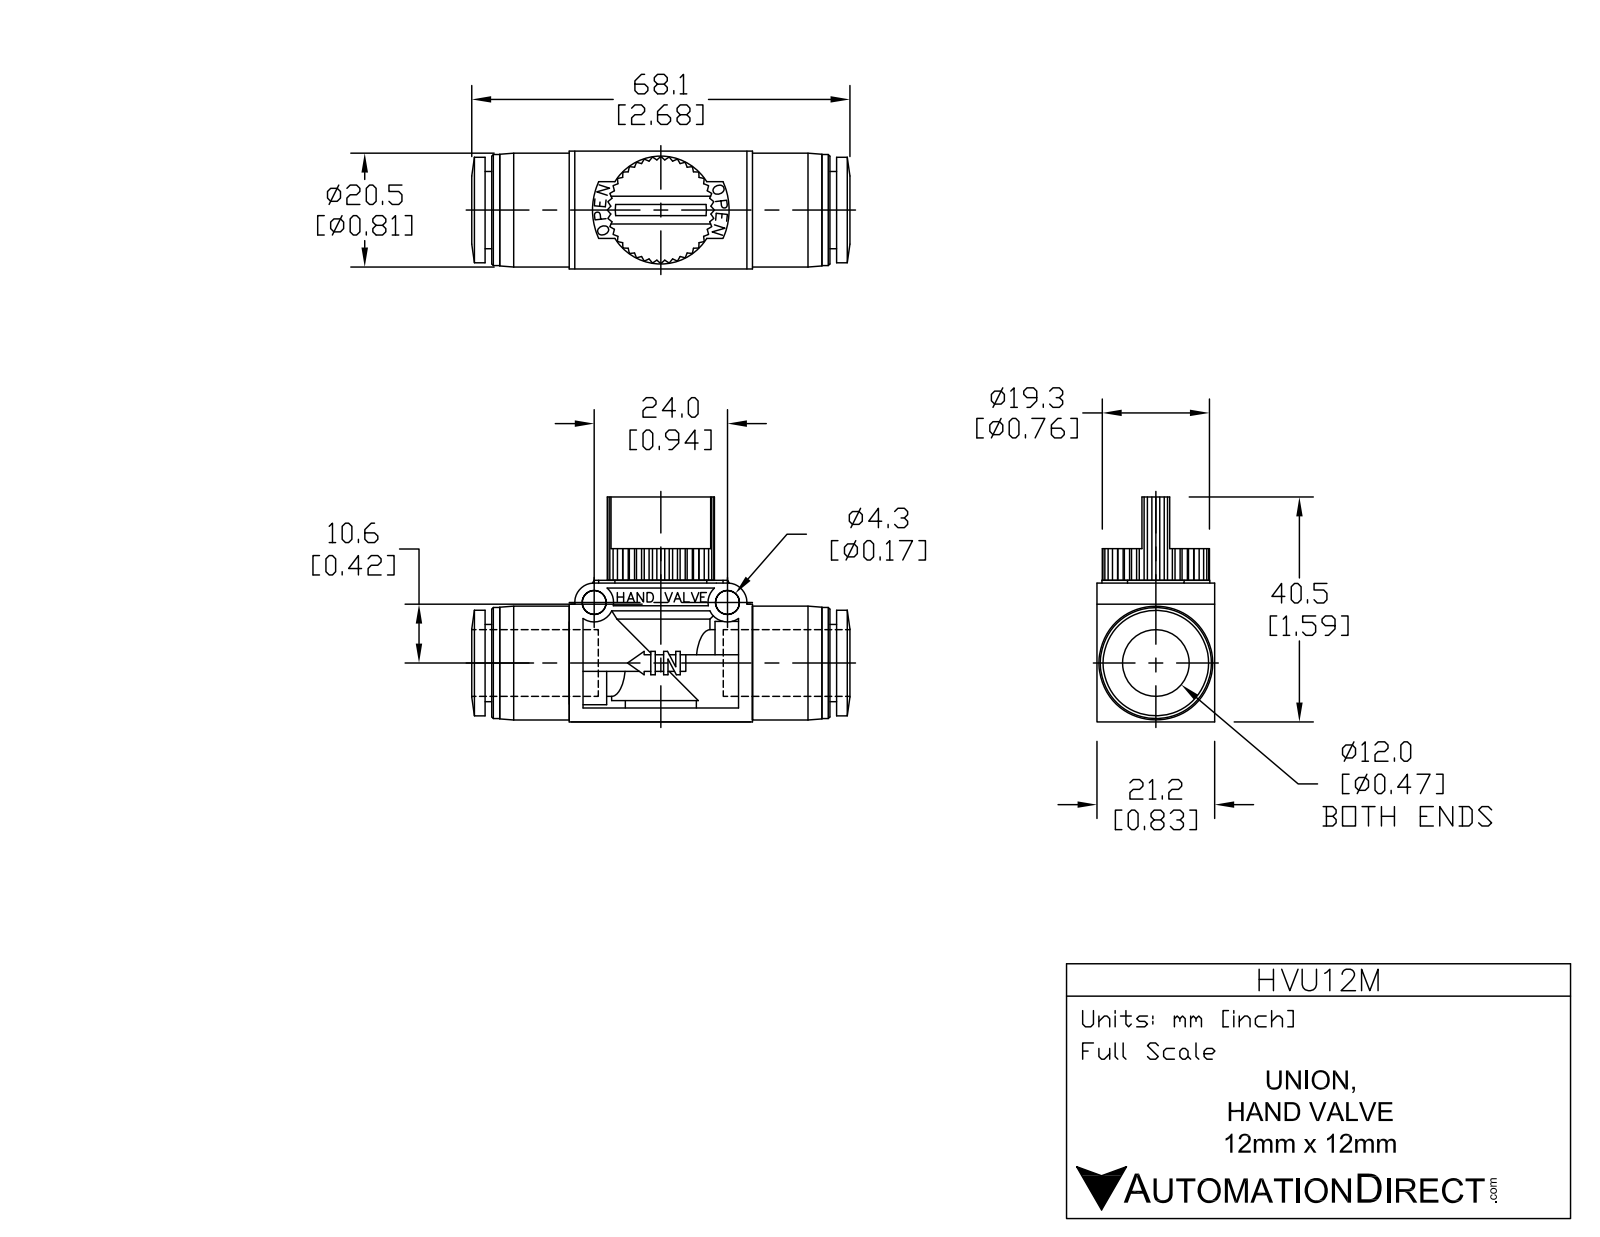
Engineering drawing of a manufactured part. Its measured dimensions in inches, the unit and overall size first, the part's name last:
Units: inches
Overall size (bounding box): 2.681 × 1.594 × 0.835
Round holes (diameter × count): ⌀0.169 ×2, ⌀0.484 ×1
Round bosses / shafts (diameter × count): ⌀0.807 ×1, ⌀0.787 ×1, ⌀0.748 ×1, ⌀0.701 ×1, ⌀0.697 ×1, ⌀0.591 ×1, ⌀0.547 ×1
Partial cylindrical surfaces — rounded edges, fillets, slot ends (radius × count): R0.138 ×2, R0.24 ×1, R0.252 ×1, R0.407 ×1
Main face-to-face distances: 0.098, 0.319, 0.059, 0.516, 0.378, 0.457, 0.047, 0.835, 0.138, 0.886
Hole centre spacings: 0.945
Volume: 1.278 in³ · Surface area: 18.19 in²
Bodies: 1 solid, 297 faces (214 planar, 60 cylindrical, 23 other)
Part name (STEP PRODUCT): HVU12M
STEP written by: SolidWorks 2015 (AUTOMOTIVE_DESIGN)
